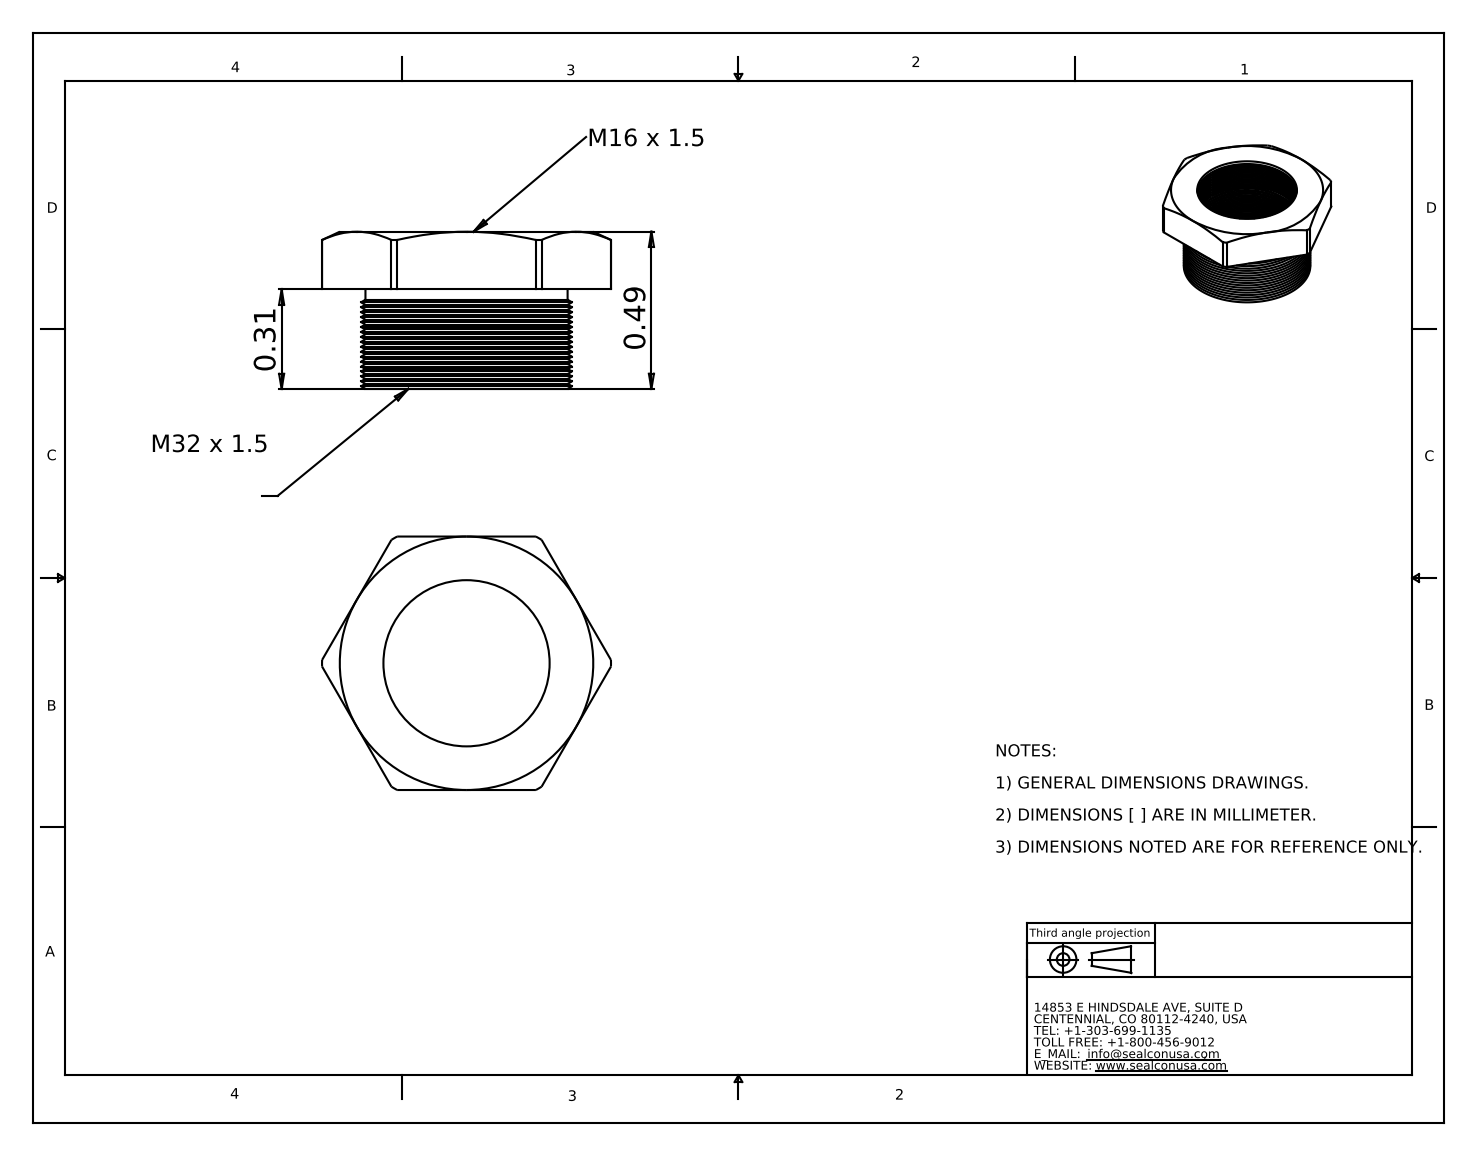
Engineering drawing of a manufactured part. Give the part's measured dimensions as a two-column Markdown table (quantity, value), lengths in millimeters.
| quantity | value |
| --- | --- |
| part name | RM-3216-SS |
| STEP written by | SolidWorks 2008 (CONFIG_CONTROL_DESIGN) |
| units | millimeters |
| bodies | 1 solid, 281 faces (9 planar, 73 cylindrical, 199 other) |
| overall size | 22.9 × 20.1 × 12.4 |
| volume | 1 500 mm³ |
| surface area | 2 537 mm² |
| round holes (diameter × count) | 13.2 × 1 |
| round bosses / shafts (diameter × count) | 16 × 1 |
| partial cylindrical surfaces (radius × count) | 11.4 × 1 |
| main face-to-face distances | 4.6, 20.1, 7.9, 12.4 |
